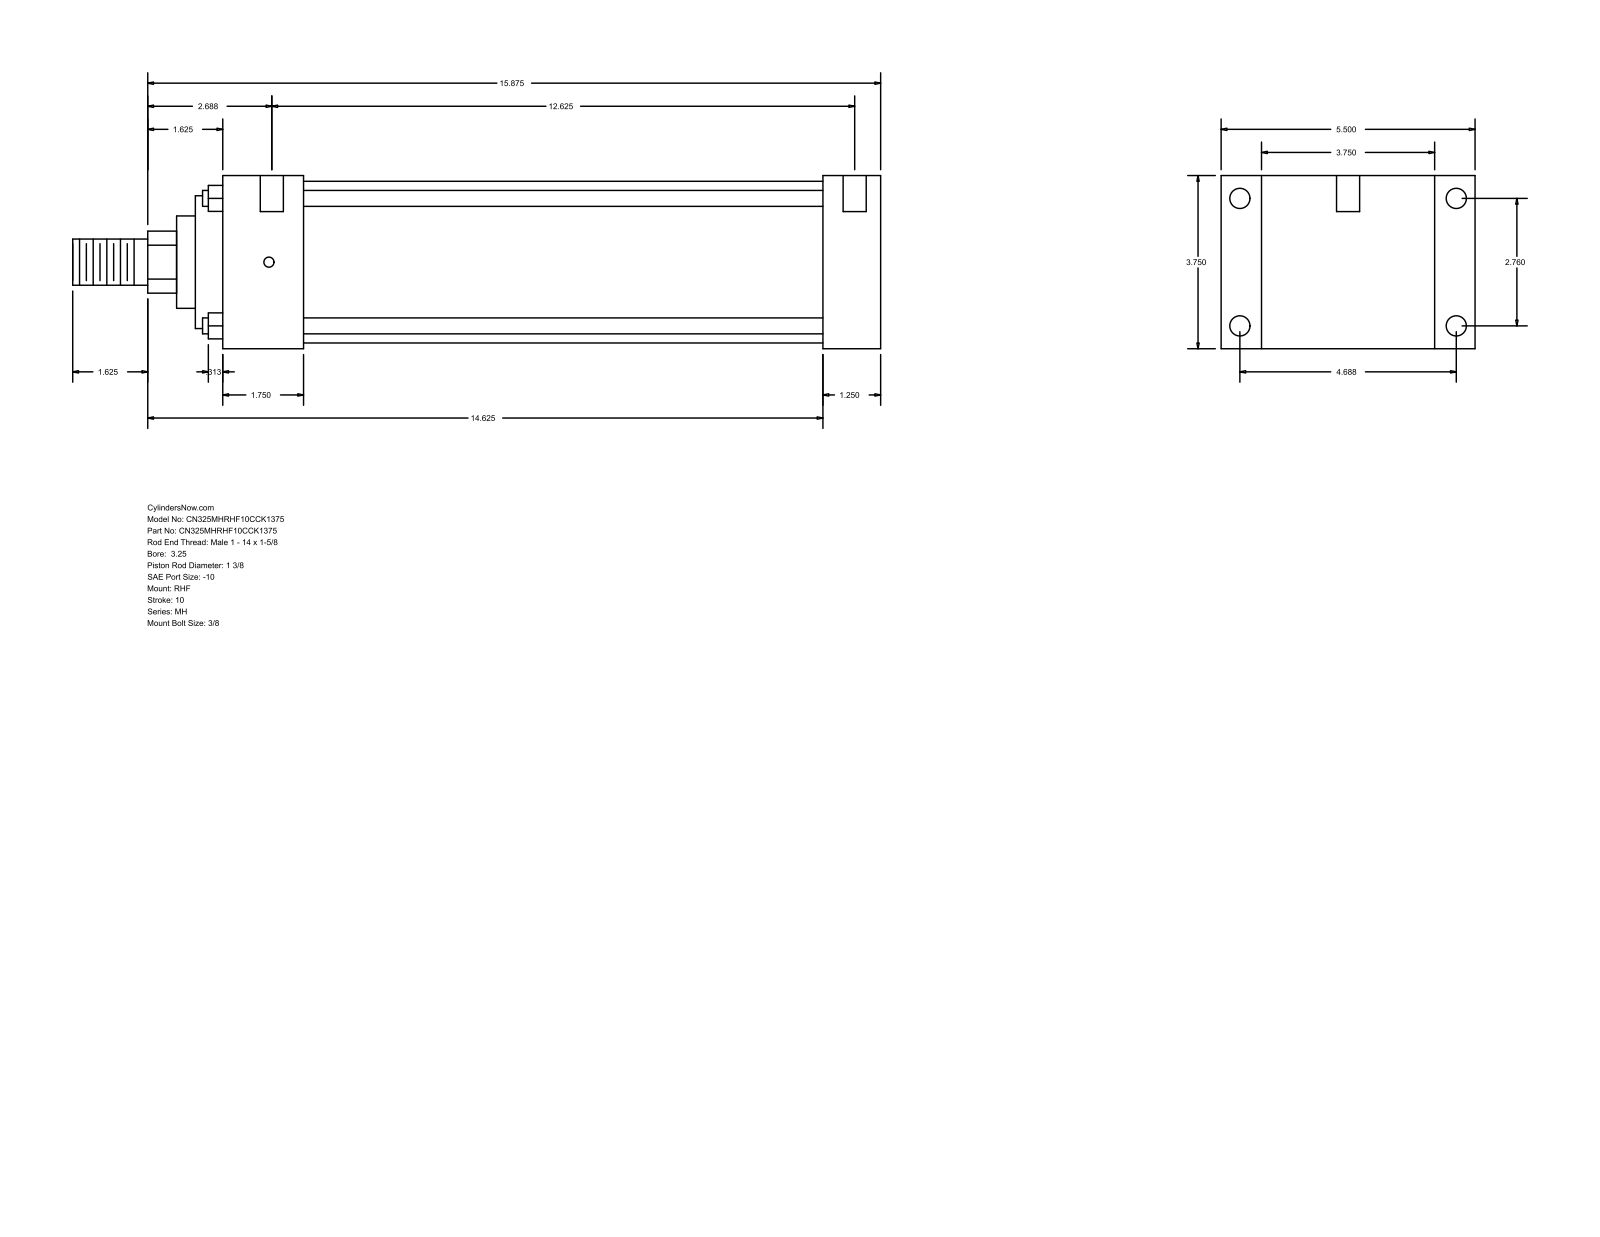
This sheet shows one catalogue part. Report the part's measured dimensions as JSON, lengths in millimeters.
{"part_name": "MH_RHF__0325_1.375", "step_written_by": "GSSL Pune (CONFIG_CONTROL_DESIGN)", "units": "millimeters", "bodies": {"solids": 0, "faces": 90, "planar": 61, "cylindrical": 29, "other": 0}, "overall_size": [444.5, 139.7, 95.25], "round_holes": [[5.56, 4], [11.13, 4], [12.7, 2]], "round_bosses_or_shafts": [[8.76, 4], [88.9, 1], [73.03, 1], [50.8, 1], [34.92, 1], [25.4, 1]], "partial_cylinders_radius": [[17.06, 1]], "face_to_face_distances": [95.24, 31.75, 22.23, 117.47, 330.21, 361.96, 139.7, 44.45, 285.76, 317.51], "hole_center_spacings": [70.1, 119.06, 138.16, 327.03, 1.59, 4.76, 320.68, 322.27]}
